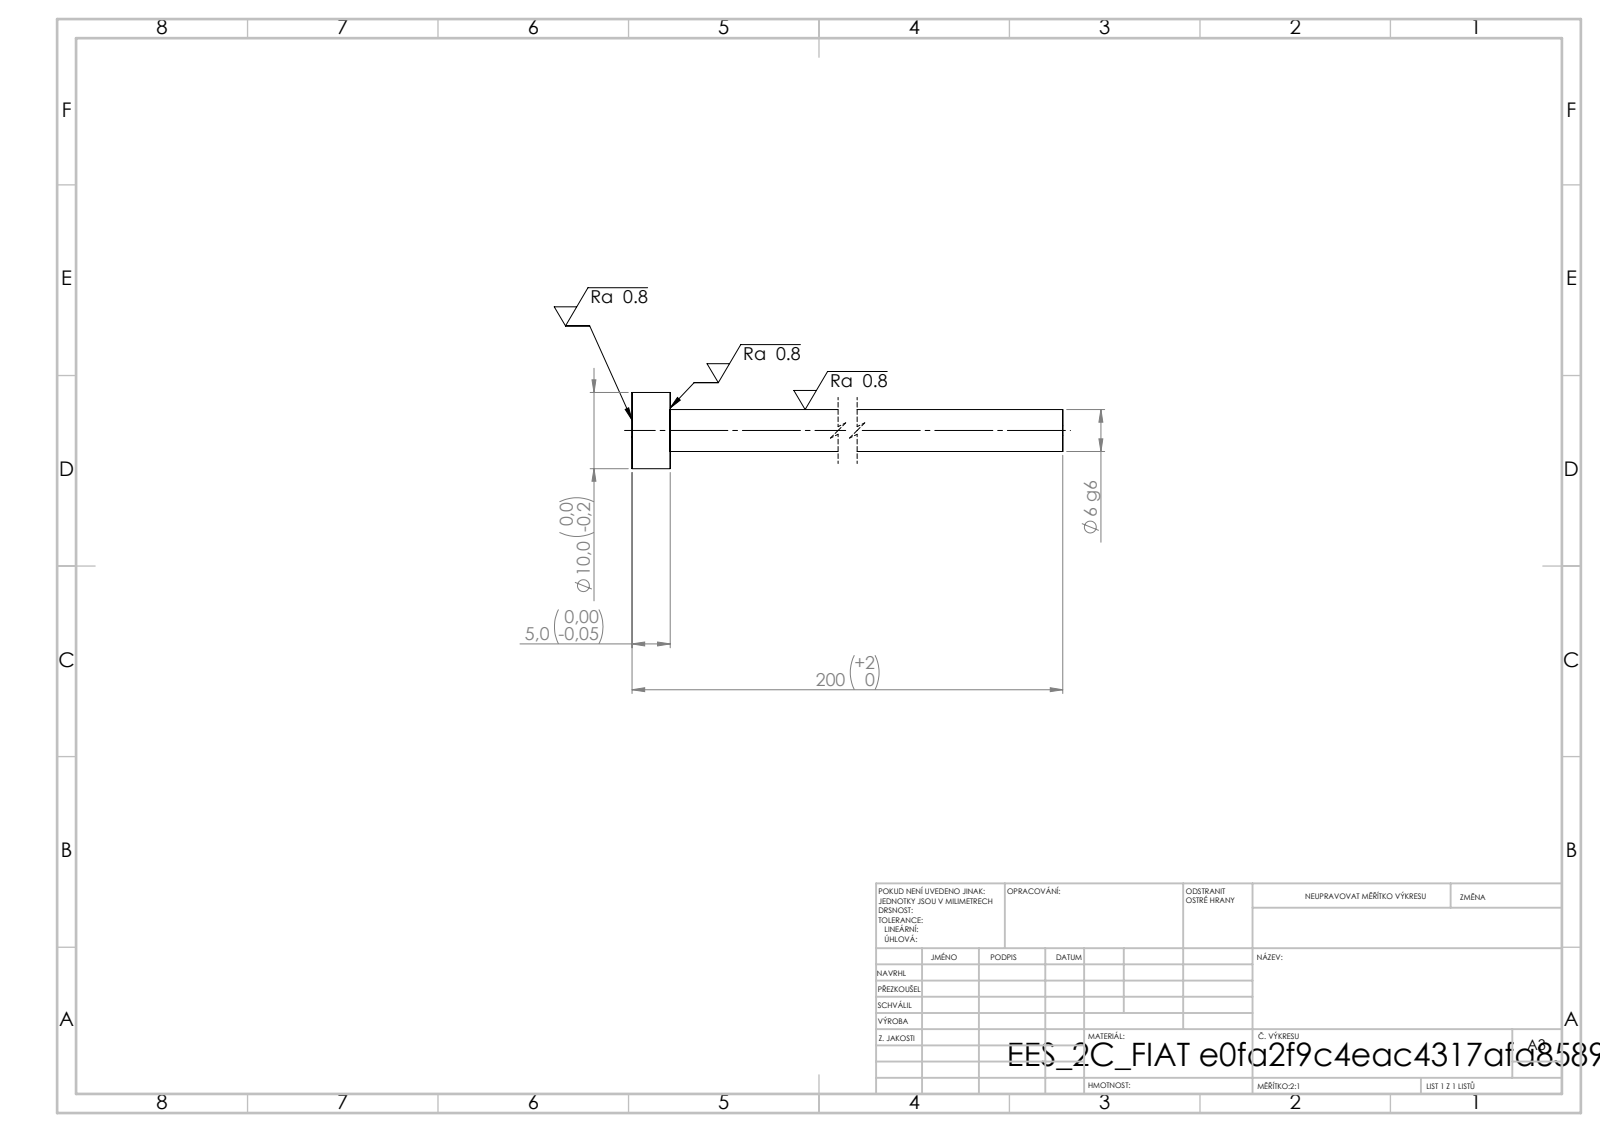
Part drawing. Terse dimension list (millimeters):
written by: SolidWorks 2019 (CONFIG_CONTROL_DESIGN)
unit: mm
bodies: 1 solid, 7 faces (3 planar, 4 cylindrical, 0 other)
size: 200 × 10 × 10
volume: 5 026 mm³; area: 3 684 mm²
bosses: 1× ⌀10, 1× ⌀5.5
face distances: 5, 200, 195
